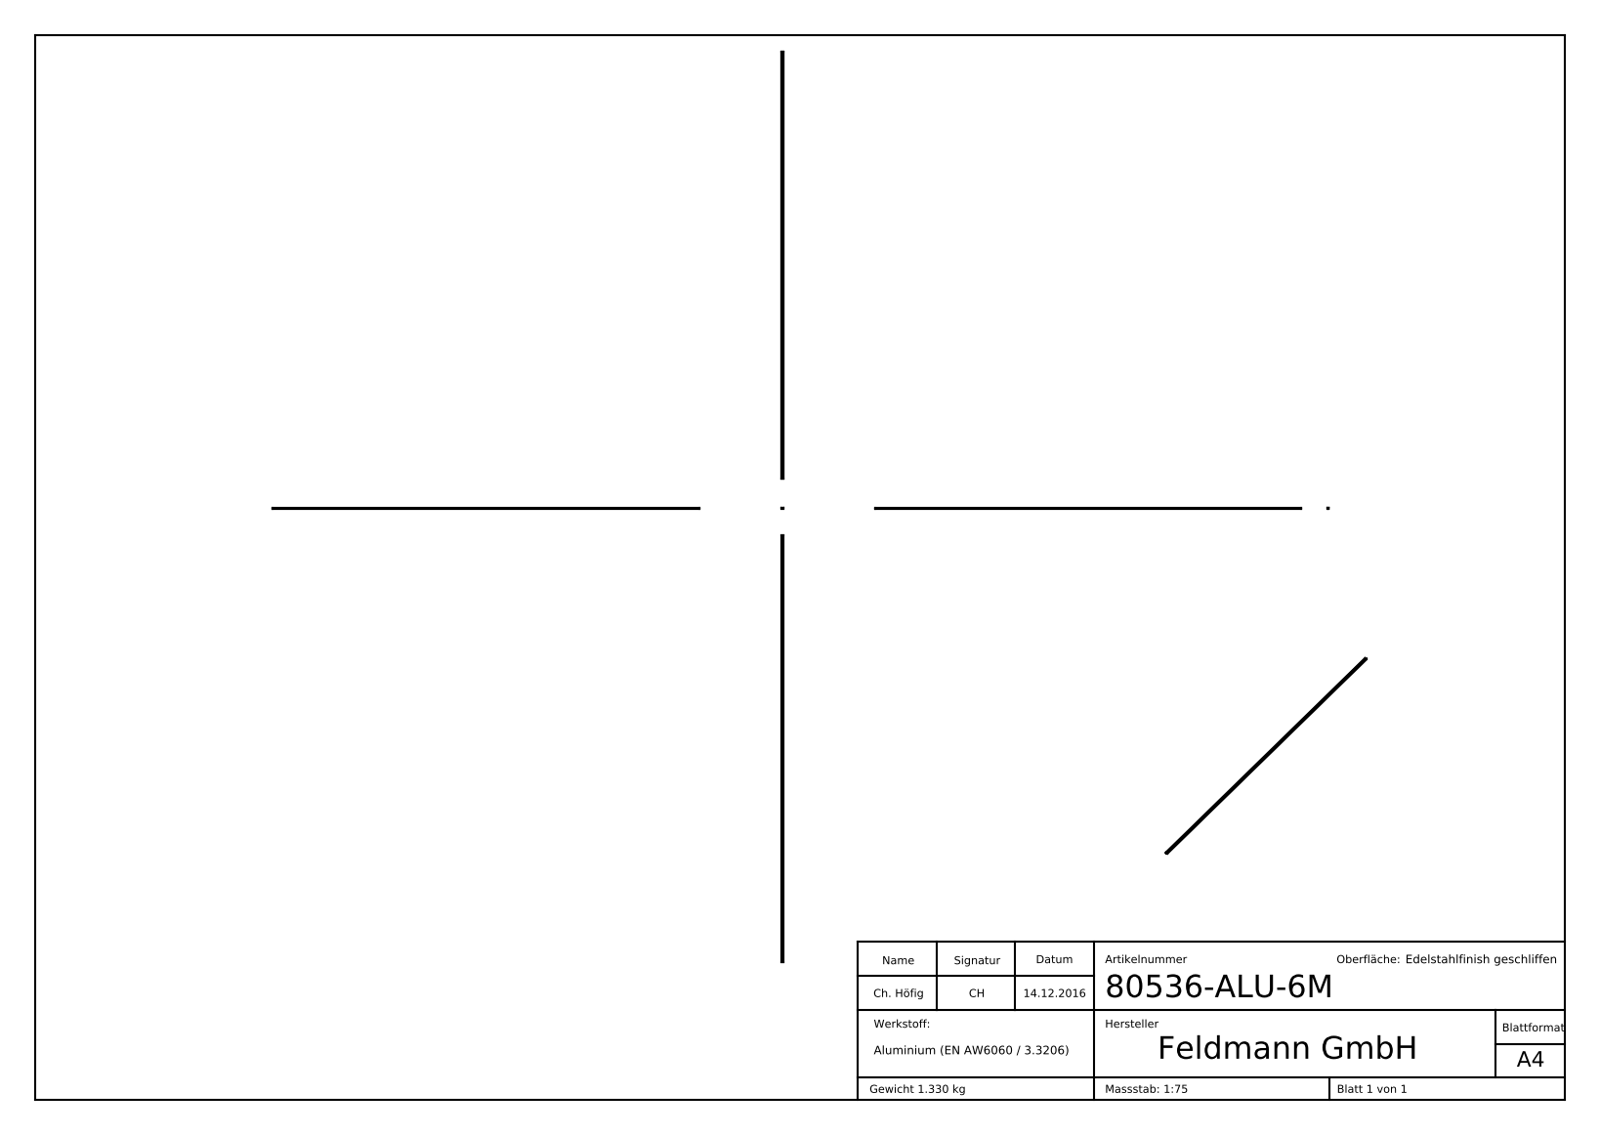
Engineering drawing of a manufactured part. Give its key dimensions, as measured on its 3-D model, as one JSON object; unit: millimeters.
{"part_name": "80536-ALU-6M", "step_written_by": "SolidWorks 2015 (CONFIG_CONTROL_DESIGN)", "units": "millimeters", "bodies": {"solids": 1, "faces": 304, "planar": 172, "cylindrical": 6, "other": 126}, "overall_size": [6000, 22, 12], "volume_mm3": 492411, "surface_area_mm2": 512729, "partial_cylinders_radius": [[0.5, 4], [2, 2]], "face_to_face_distances": [2, 20, 22, 18, 10, 12, 6000, 1.9, 18.1, 20.1]}
